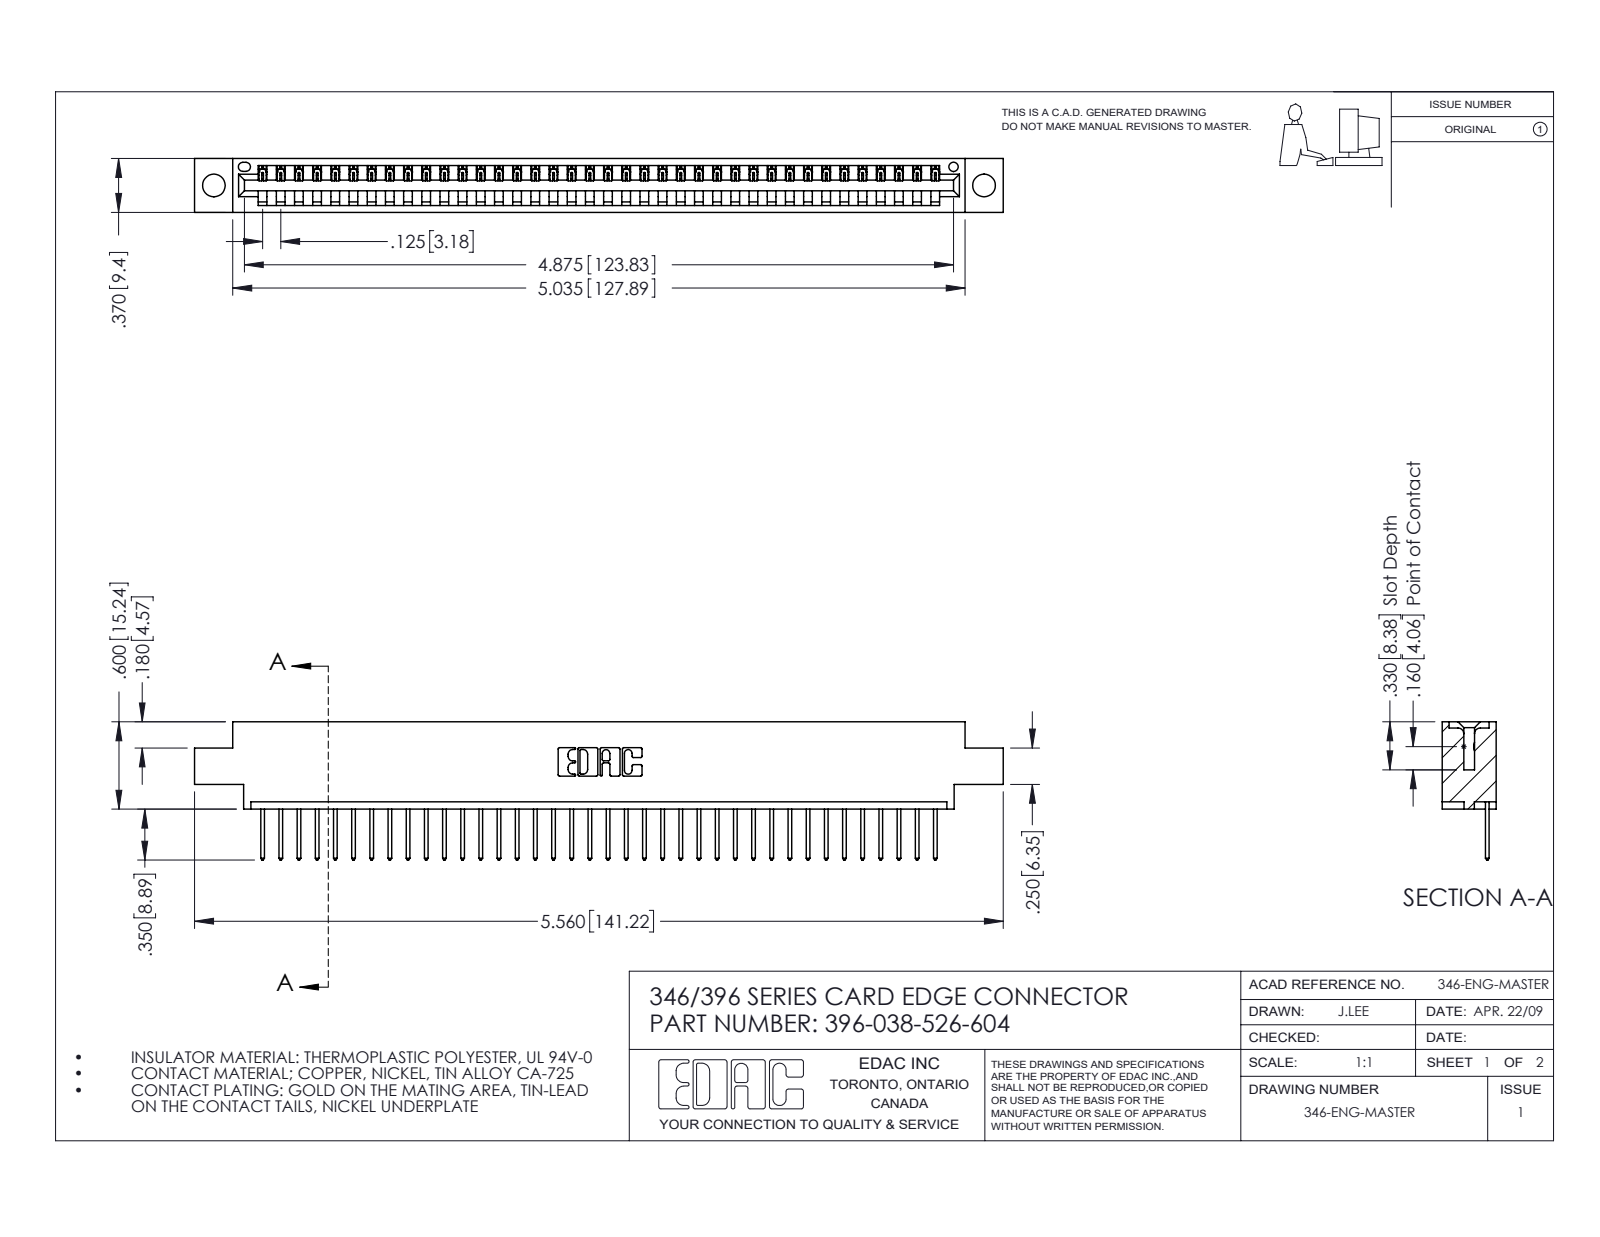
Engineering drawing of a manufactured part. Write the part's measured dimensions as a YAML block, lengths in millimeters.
part_name: "346 Part_0.170 Offset - 0.156 Dia-TH; 396-038-526-604; 345-292-001_345-293-126"
step_written_by: "SolidWorks 2016 (CONFIG_CONTROL_DESIGN)"
units: millimeters
bodies: {solids: 39, faces: 2330, planar: 1600, cylindrical: 730, other: 0}
overall_size: [141.2, 24.1, 9.4]
volume: 13200
surface_area: 16410
round_holes:
  - {diameter: 4, count: 2}
  - {diameter: 1.6, count: 1}
partial_cylinders:
  - {radius: 0.2, count: 76}
  - {radius: 0.3, count: 76}
  - {radius: 0.3, count: 22}
  - {radius: 0.2, count: 6}
  - {radius: 0.8, count: 6}
  - {radius: 0.7, count: 3}
  - {radius: 0.8, count: 2}
  - {radius: 1, count: 2}
face_to_face_distances: [1.2, 8.2, 9.4, 6.4, 1.8, 7.6, 0.6, 3.8, 5.6, 2.5]
hole_center_spacings: [6.2, 129.2, 134.5]
